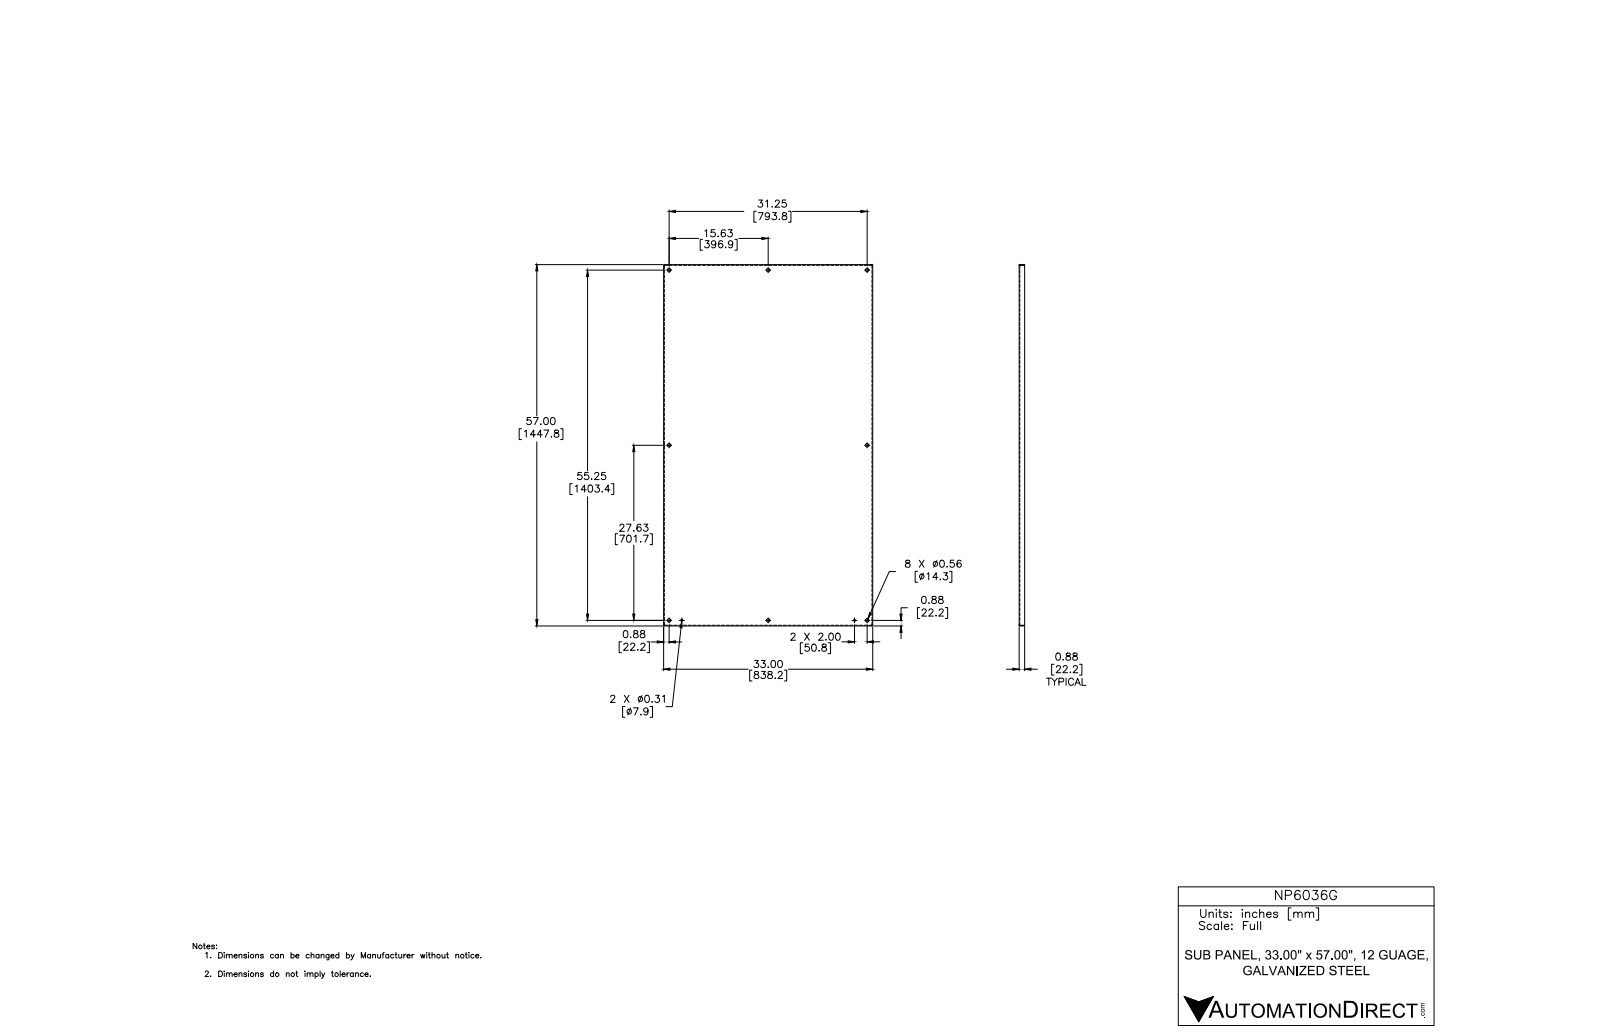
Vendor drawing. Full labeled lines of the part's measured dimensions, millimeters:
Part name (STEP PRODUCT): NP6036G
STEP written by: Autodesk Inventor 2012 (AUTOMOTIVE_DESIGN)
Units: millimetres
Bodies: 1 solid, 48 faces (22 planar, 18 cylindrical, 8 other)
Overall size (bounding box): 1447.8 × 838.2 × 22.2
Volume: 3 091 000 mm³ · Surface area: 2 610 000 mm²
Round holes (diameter × count): ⌀14.3 ×8, ⌀7.9 ×2
Partial cylindrical surfaces — rounded edges, fillets, slot ends (radius × count): R0.8 ×4, R3.2 ×4
Main face-to-face distances: 2.4, 835.8, 1445.4, 838.2, 833.5, 1447.8, 1443.1, 19.8, 22.2, 2.7
Hole centre spacings: 701.7, 806.1, 1458.4, 1403.4, 50.8, 396.9, 396.9, 703.5
